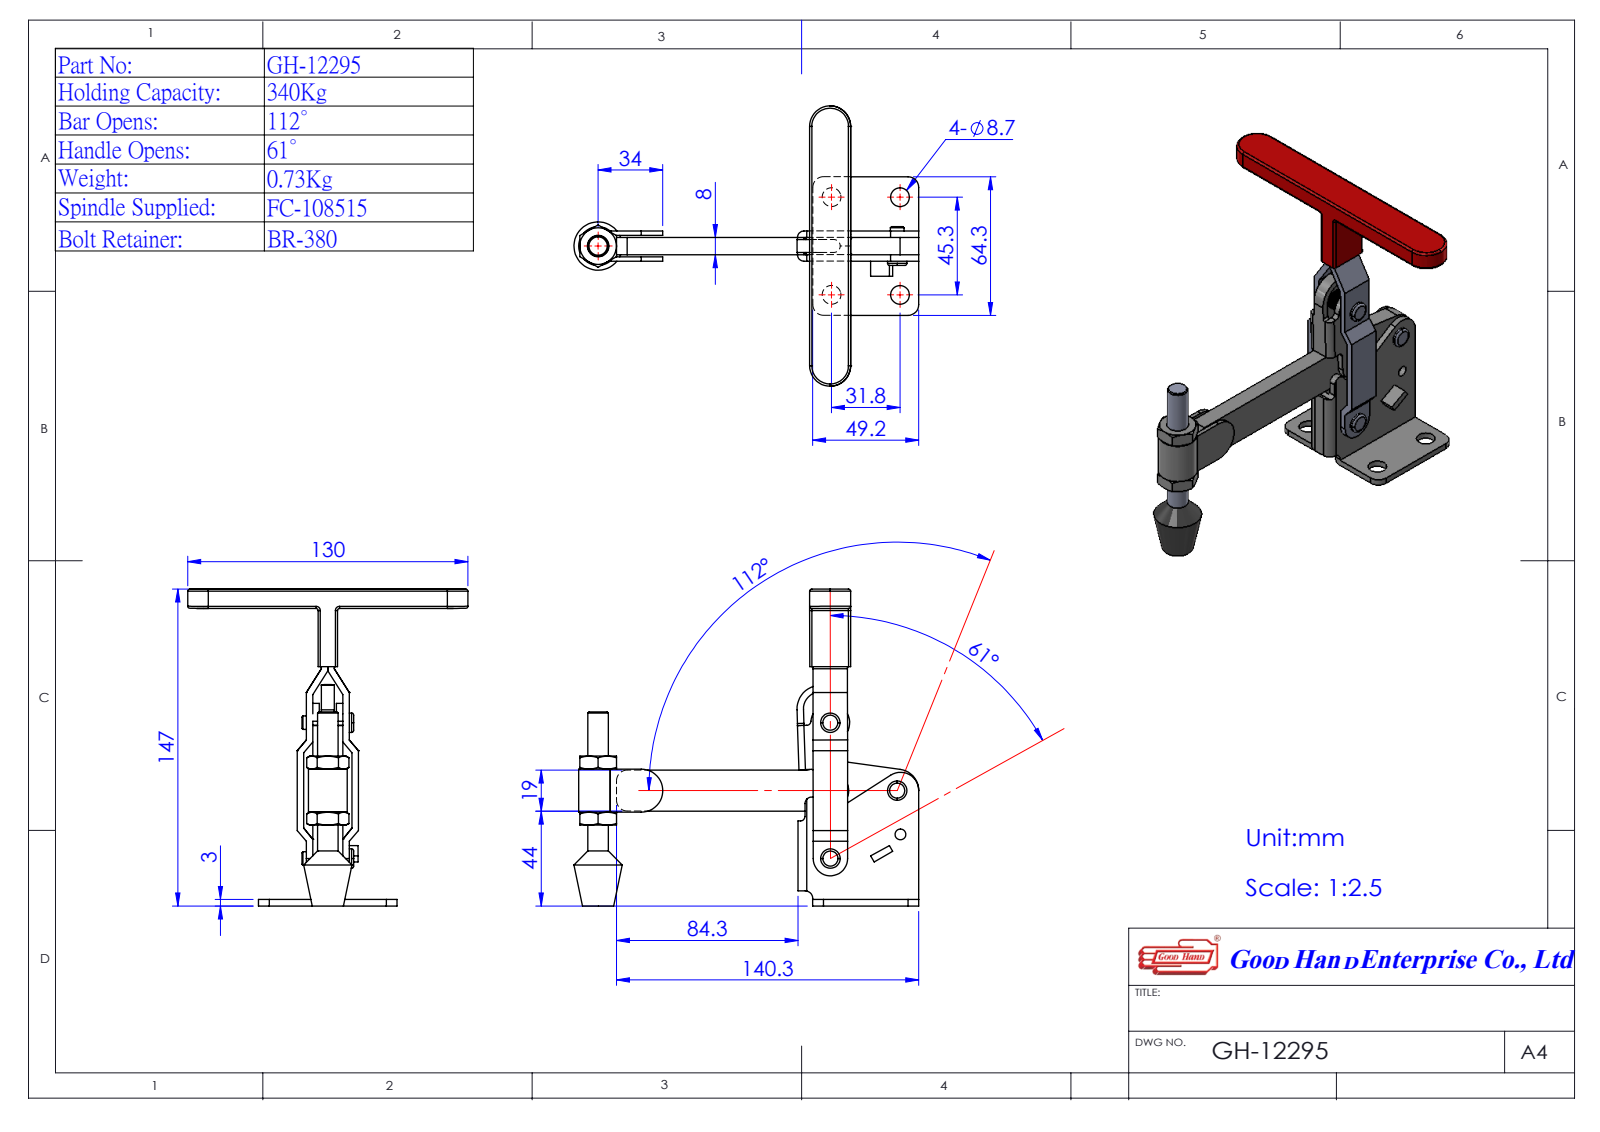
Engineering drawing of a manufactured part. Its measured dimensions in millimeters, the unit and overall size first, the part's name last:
Units: millimetres
Overall size (bounding box): 172.09 × 146.8 × 130
Round holes (diameter × count): ⌀6 ×4, ⌀8.7 ×4
Round bosses / shafts (diameter × count): ⌀9.01 ×4, ⌀6.28 ×4, ⌀9.53 ×1
Partial cylindrical surfaces — rounded edges, fillets, slot ends (radius × count): R1 ×14, R5 ×6, R2 ×4, R2.02 ×2, R8 ×2, R8.5 ×2, R9 ×2, R9.5 ×2
Main face-to-face distances: 3, 11, 8, 14, 7.2, 18.2, 21.2, 0.5, 4.2, 8.79
Hole centre spacings: 31.52, 31.8, 45.3, 55.35, 30, 44.2, 44.24, 63
Volume: 106 330 mm³ · Surface area: 56 820 mm²
Bodies: 5 solids, 302 faces (132 planar, 118 cylindrical, 52 other)
Part name (STEP PRODUCT): Group2^GH-12295(簡化); GH-12295(簡化); Group5^GH-12295(簡化); Group4^GH-12275(簡化)-1 (+2 more)
STEP written by: SolidWorks 2016 (AUTOMOTIVE_DESIGN)
